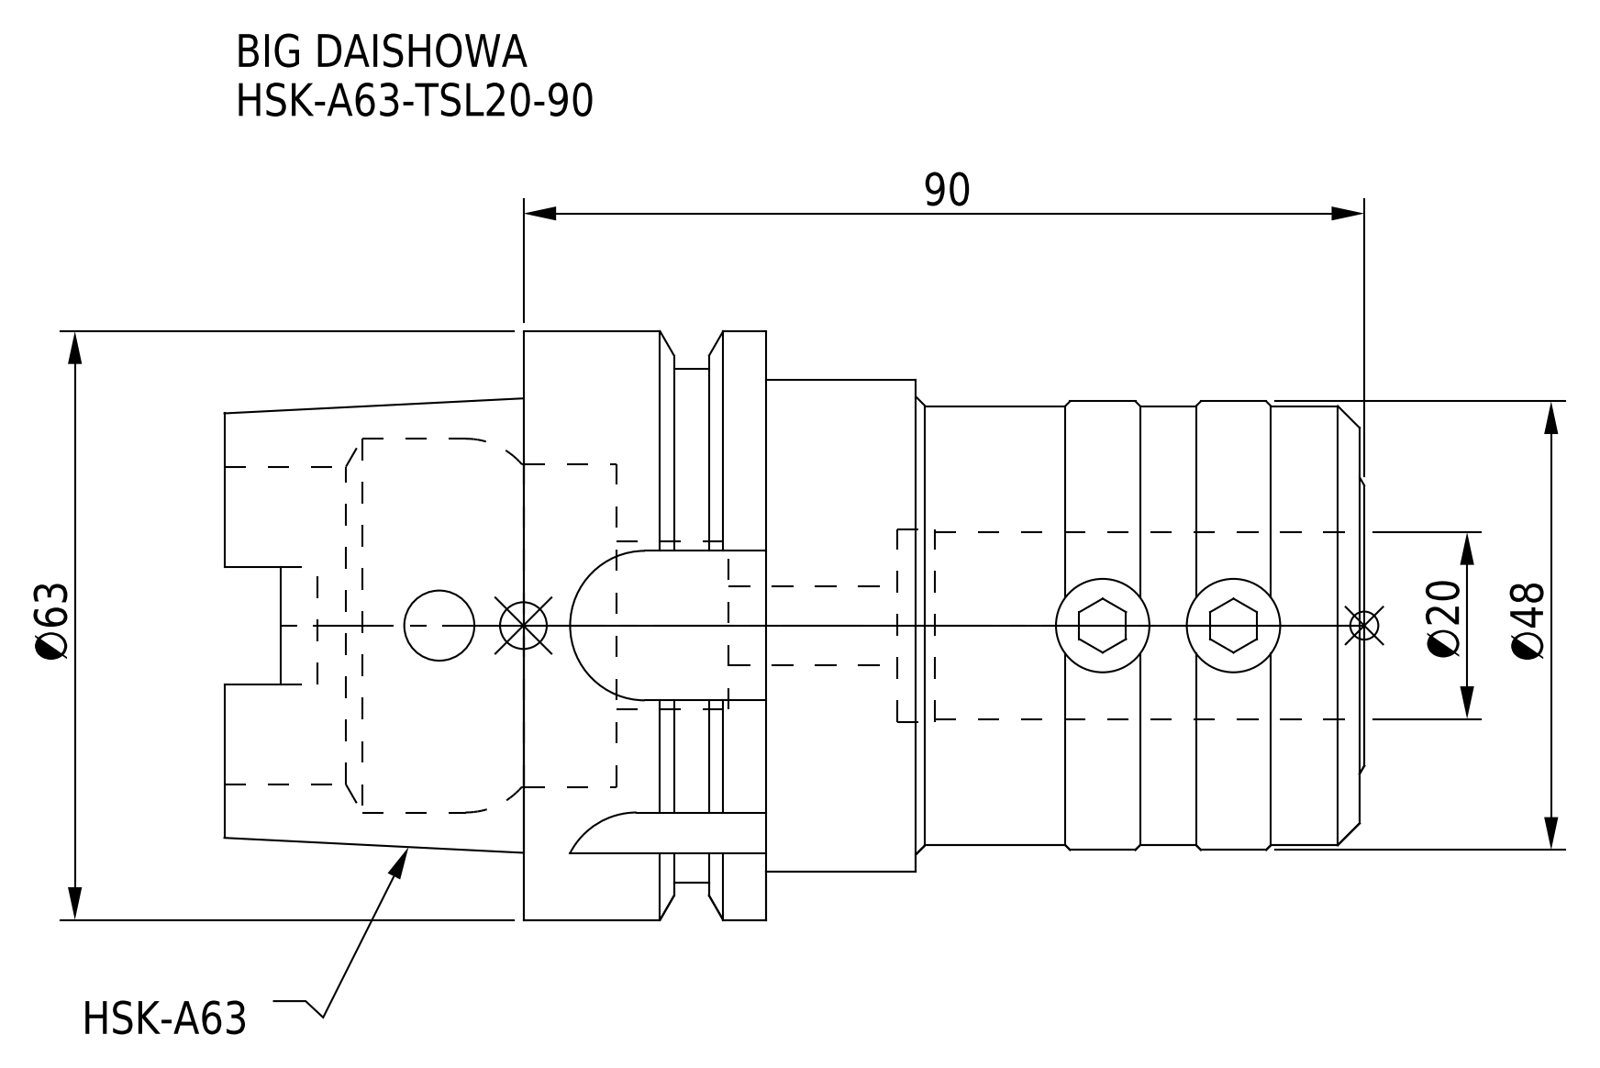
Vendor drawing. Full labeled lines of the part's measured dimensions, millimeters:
Part name (STEP PRODUCT): HSK-A63-TSL20-90
STEP written by: CREO PARAMETRIC BY PTC INC, 2016380 (AUTOMOTIVE_DESIGN)
Units: millimetres
Bodies: 1 solid, 115 faces (40 planar, 47 cylindrical, 28 other)
Overall size (bounding box): 122 × 63 × 63
Volume: 183 393 mm³ · Surface area: 35 416 mm²
Round holes (diameter × count): ⌀7.5 ×1, ⌀8.4 ×1, ⌀18 ×1, ⌀20 ×1, ⌀20.6 ×1, ⌀34 ×1, ⌀34.5 ×1, ⌀40 ×1
Round bosses / shafts (diameter × count): ⌀63 ×1, ⌀55 ×1, ⌀52.6 ×1, ⌀48 ×1, ⌀47 ×1
Partial cylindrical surfaces — rounded edges, fillets, slot ends (radius × count): R2.88 ×4, R8 ×4
Main face-to-face distances: 26, 16.05, 9.95, 63.5, 79.55, 89.5, 64, 121.5, 58, 41.95
